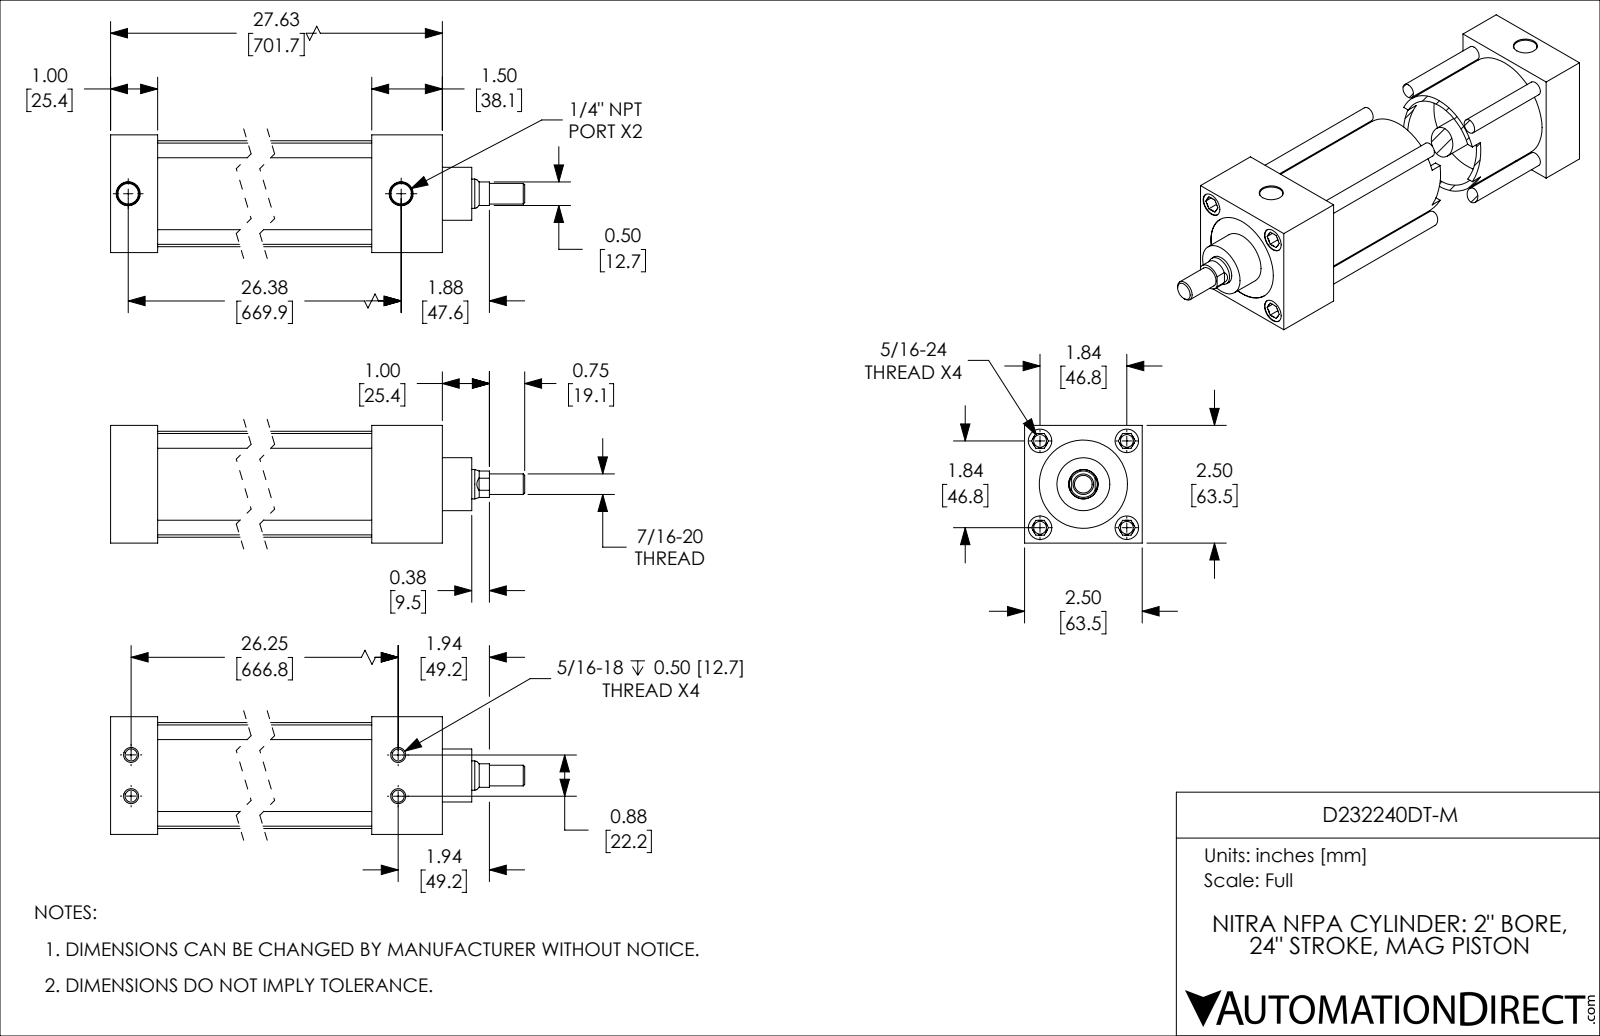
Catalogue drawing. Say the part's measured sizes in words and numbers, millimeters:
The part is named "D232240DT-M_PISTON_KK1; D232240DT-M; D232240DT-M_BODY". Its 3-D file was written by "SolidWorks 2019 (CONFIG_CONTROL_DESIGN)". It is 2 solids with 200 faces: 58 planar, 62 cylindrical and 80 other. Overall it measures 746.1 by 63.5 by 63.5 millimeters. Its volume is 904 100 cubic millimeters and its surface area 363 600 square millimeters. Round holes: 7 of diameter 6.9, 4 of diameter 6.5, 4 of diameter 12.7, 2 of diameter 11.1, 1 of diameter 15.9, 1 of diameter 47.6, 1 of diameter 50.8. Round bosses or shafts: 4 of diameter 7.9, 1 of diameter 57.2, 1 of diameter 50.8, 1 of diameter 28.6, 1 of diameter 15.8, 1 of diameter 11.1. Partial cylindrical surfaces (rounded edges, fillets, slot ends): 1 of radius 7.1. The main face-to-face distances are 63.5, 25.4, 663.6, 638.2, 28.6, 54, 609.6, 38.1, 701.7, 676.3. The hole center spacings are 46.7, 46.8, 33, 11.2, 11.3, 22.2, 33.1, 66.1.
